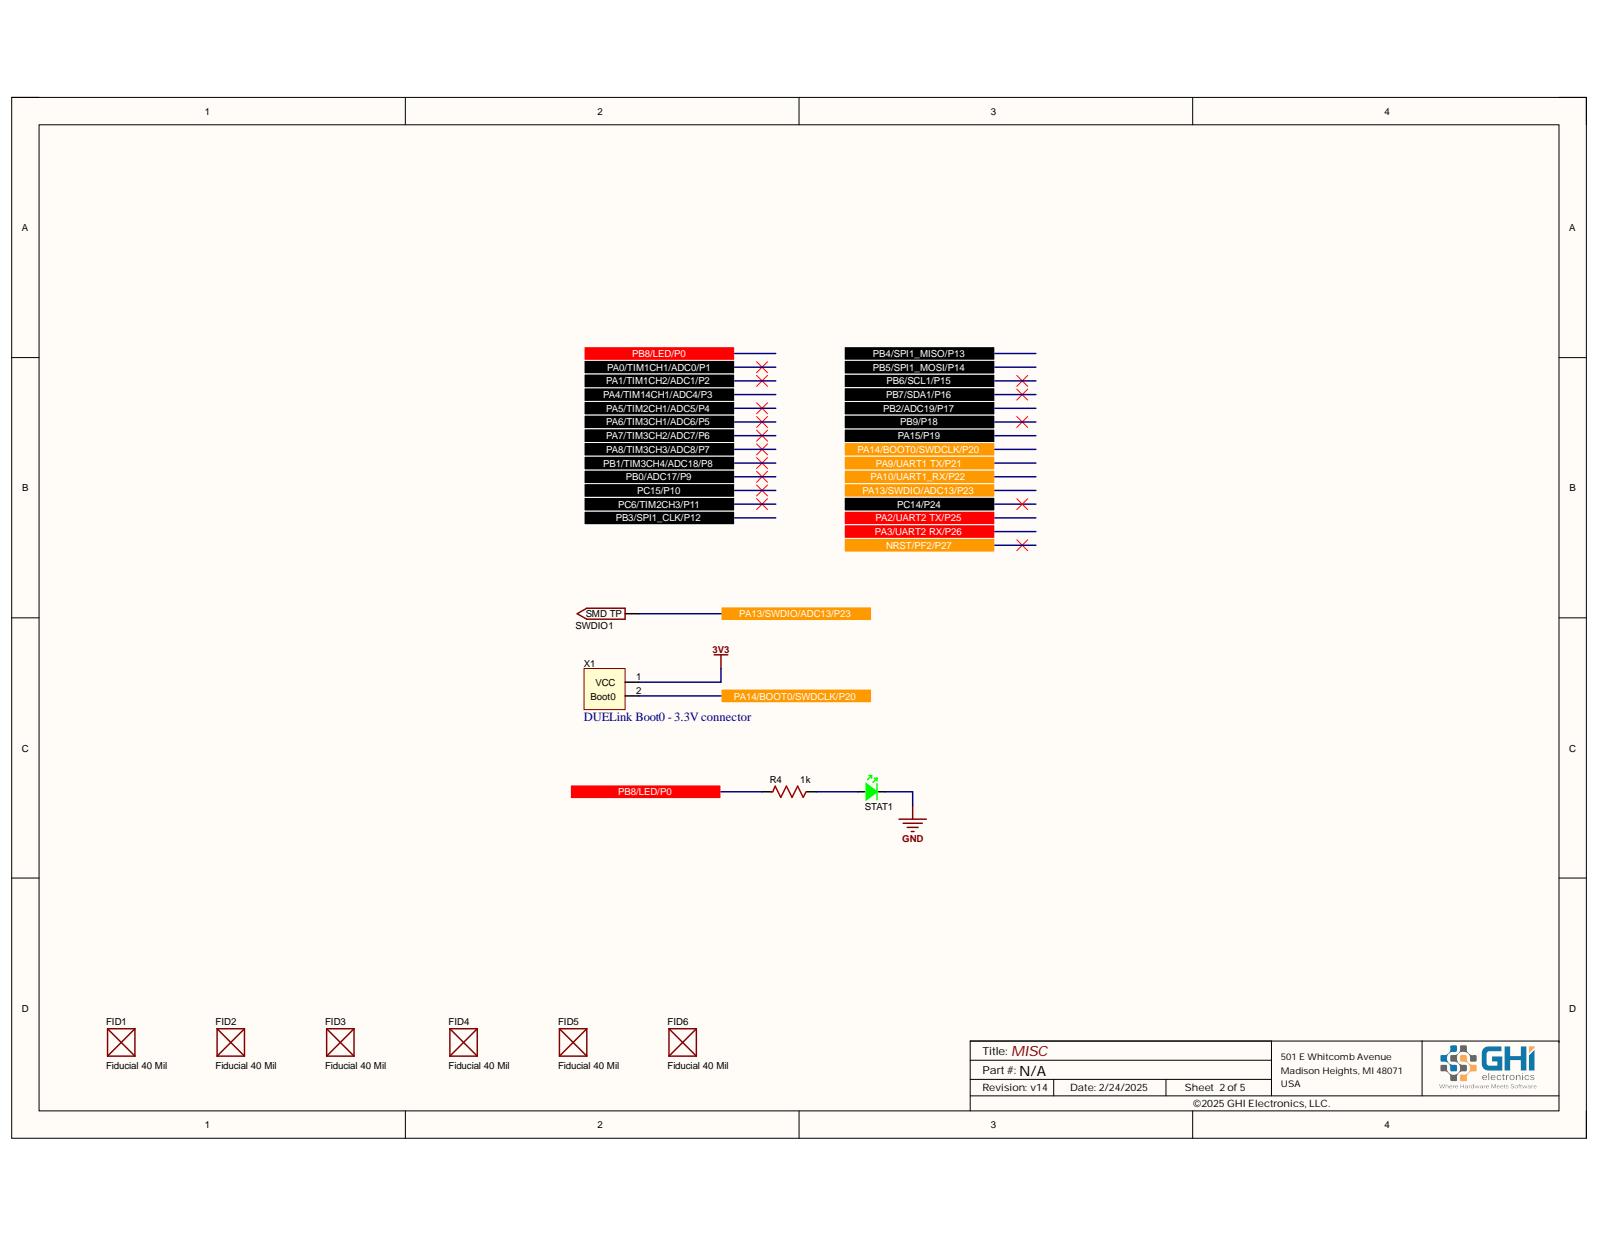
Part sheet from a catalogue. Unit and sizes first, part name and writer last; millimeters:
Units: millimetres
Overall size (bounding box): 47 × 32 × 7.27
Round holes (diameter × count): ⌀3 ×4, ⌀1.02 ×2, ⌀1.5 ×2
Round bosses / shafts (diameter × count): ⌀1.4 ×1, ⌀0.8 ×1
Partial cylindrical surfaces — rounded edges, fillets, slot ends (radius × count): R0.12 ×35, R0.15 ×20, R1 ×5, R0.2 ×4, R0.35 ×4, R0.75 ×4, R3.5 ×4, R0.1 ×2
Main face-to-face distances: 2.65, 2.85, 2.45, 0.5, 2.15, 2.35, 1, 28.5, 0.69, 1.05
Hole centre spacings: 5.59, 19.6, 25, 40, 47.17, 2.54, 7.03, 7.67
Volume: 1 040 mm³ · Surface area: 6 199 mm²
Bodies: 81 solids, 1419 faces (1136 planar, 236 cylindrical, 47 other)
Part name (STEP PRODUCT): PCB; Board; STAT1; 0603 LED Green (+5 more)
STEP written by: Open CASCADE 7.5 (AUTOMOTIVE_DESIGN)
